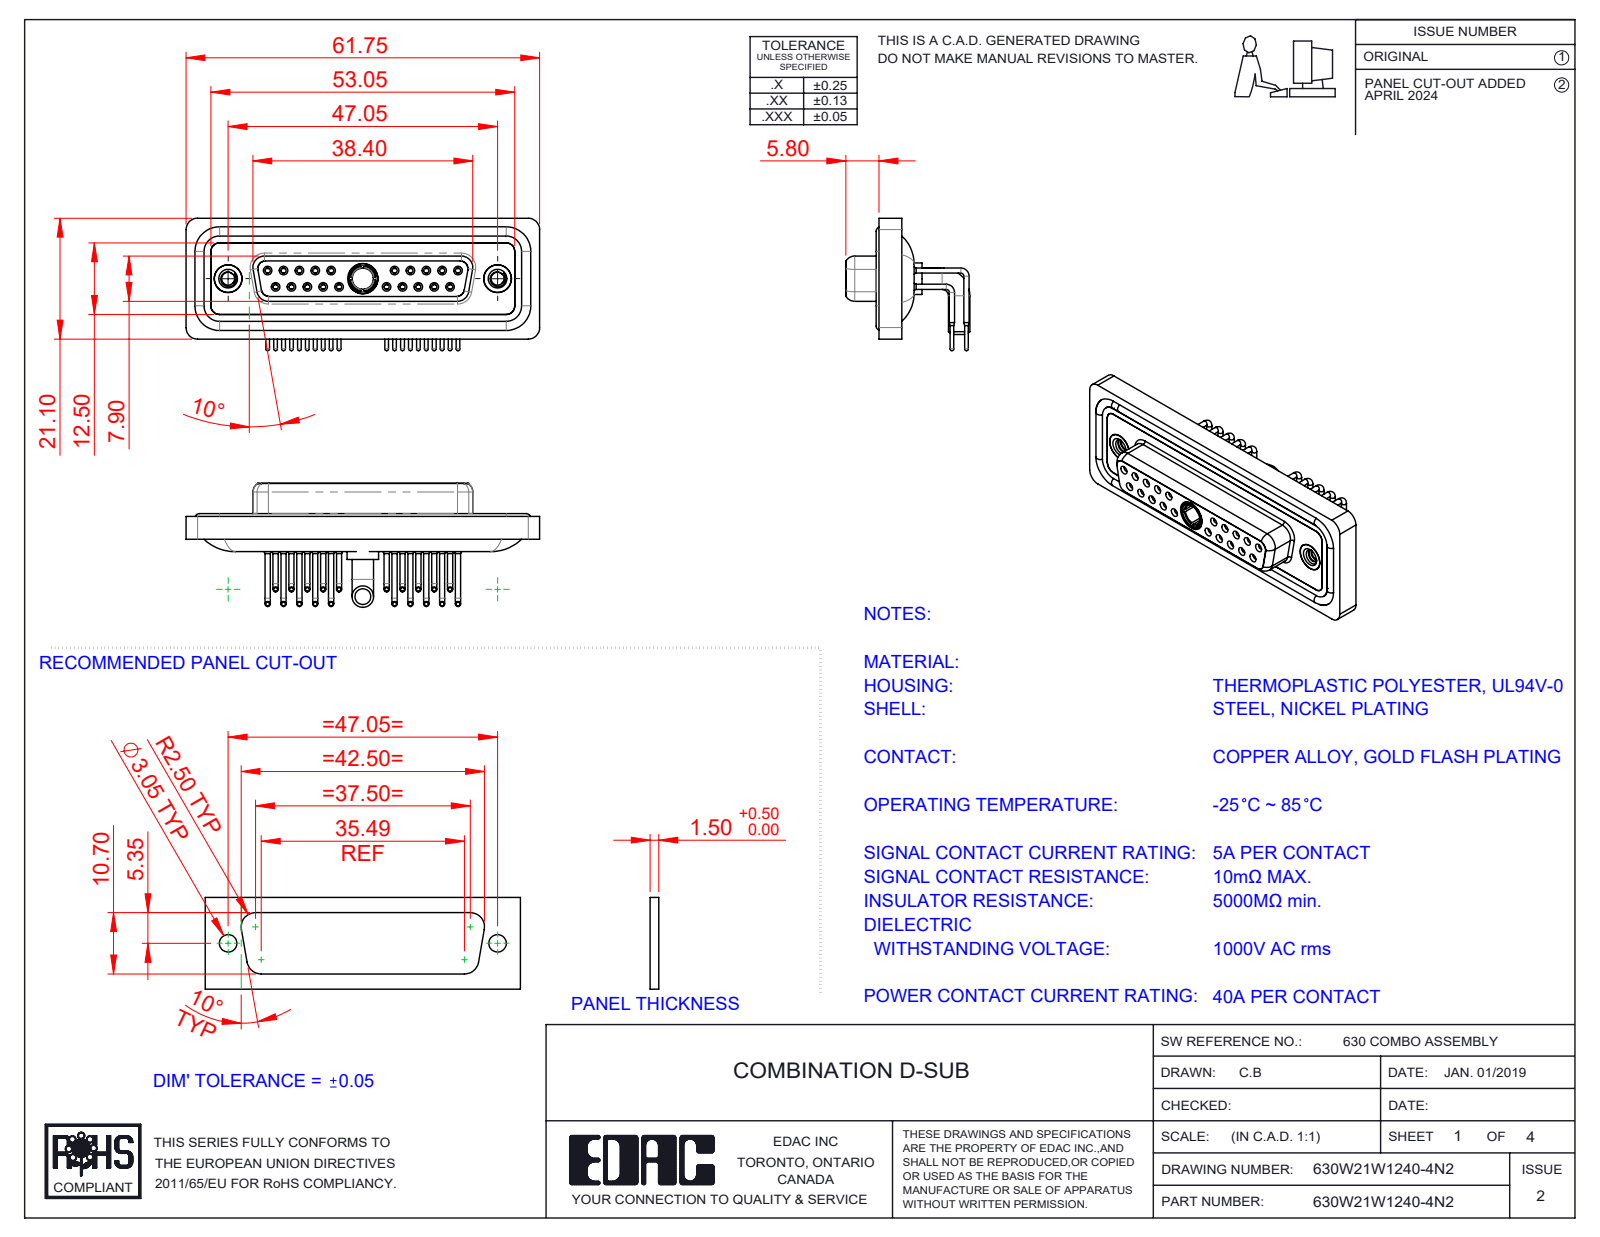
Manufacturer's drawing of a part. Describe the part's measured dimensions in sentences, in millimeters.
The part is named "630Combo Waterproof Housing_25 Contacts; 630Combo Shell Rear_25 Contacts; 630Combo Contact Row 2_50 Contacts; 630Combo Housing_21W1 (+5 more)". Its 3-D file was written by "SolidWorks 2023 (CONFIG_CONTROL_DESIGN)". It is 29 solids with 1524 faces: 434 planar, 673 cylindrical and 417 other. Overall it measures 61.75 by 23.12 by 21.68 millimeters. Its volume is 8 578 cubic millimeters and its surface area 14 823 square millimeters. Round holes: 20 of diameter 0.9, 20 of diameter 1.1, 20 of diameter 1.5, 20 of diameter 2, 10 of diameter 1.6, 10 of diameter 1.7, 3 of diameter 4.85, 2 of diameter 2.26, 2 of diameter 4, 2 of diameter 4.05, 2 of diameter 5, 1 of diameter 3.7. Round bosses or shafts: 20 of diameter 0.9, 20 of diameter 0.65, 14 of diameter 1.6, 2 of diameter 4.95, 2 of diameter 4.8, 2 of diameter 3.75, 1 of diameter 5.5, 1 of diameter 5.2. Partial cylindrical surfaces (rounded edges, fillets, slot ends): 18 of radius 1.5, 18 of radius 2, 8 of radius 1.35, 8 of radius 1.6, 4 of radius 0.25, 4 of radius 0.5, 4 of radius 0.6, 4 of radius 0.65. The main face-to-face distances are 0.4, 1.8, 4.1, 1.6, 1.1, 2.5, 3.1, 1.5, 9.8, 0.45. The hole center spacings are 3.16, 2.77, 5.54, 8.31, 5.04, 19.39, 20.97, 22.16.
